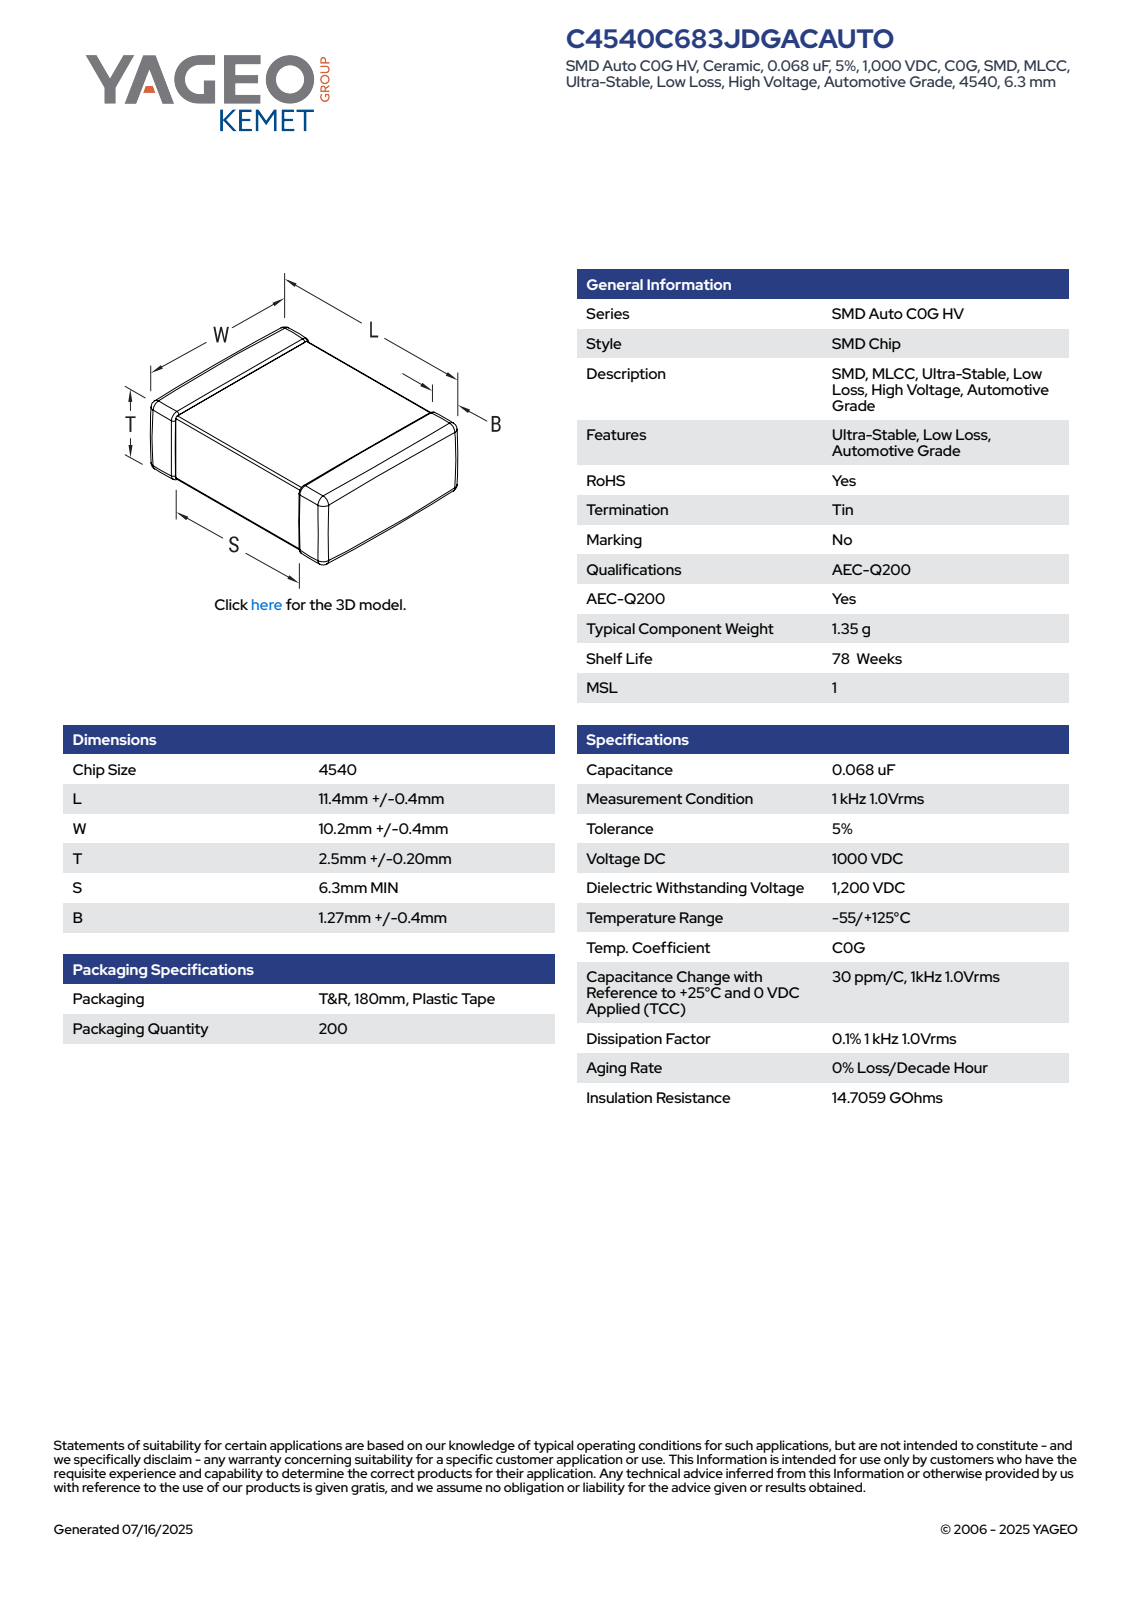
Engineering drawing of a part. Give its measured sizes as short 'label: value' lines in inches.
name: CCS_CCSTD_4540_L11.8W10.6T2.7B1.27
written by: SolidWorks 2021 (AUTOMOTIVE_DESIGN)
unit: in
bodies: 4 solids, 125 faces (71 planar, 38 cylindrical, 16 other)
size: 0.465 × 0.417 × 0.106
volume: 0.018 in³; area: 0.57 in²
rounds: 24× R0.009
face distances: 0.089, 0.098, 0.106, 0.465, 0.4, 0.409, 0.417, 0.189, 0.275, 0.251
